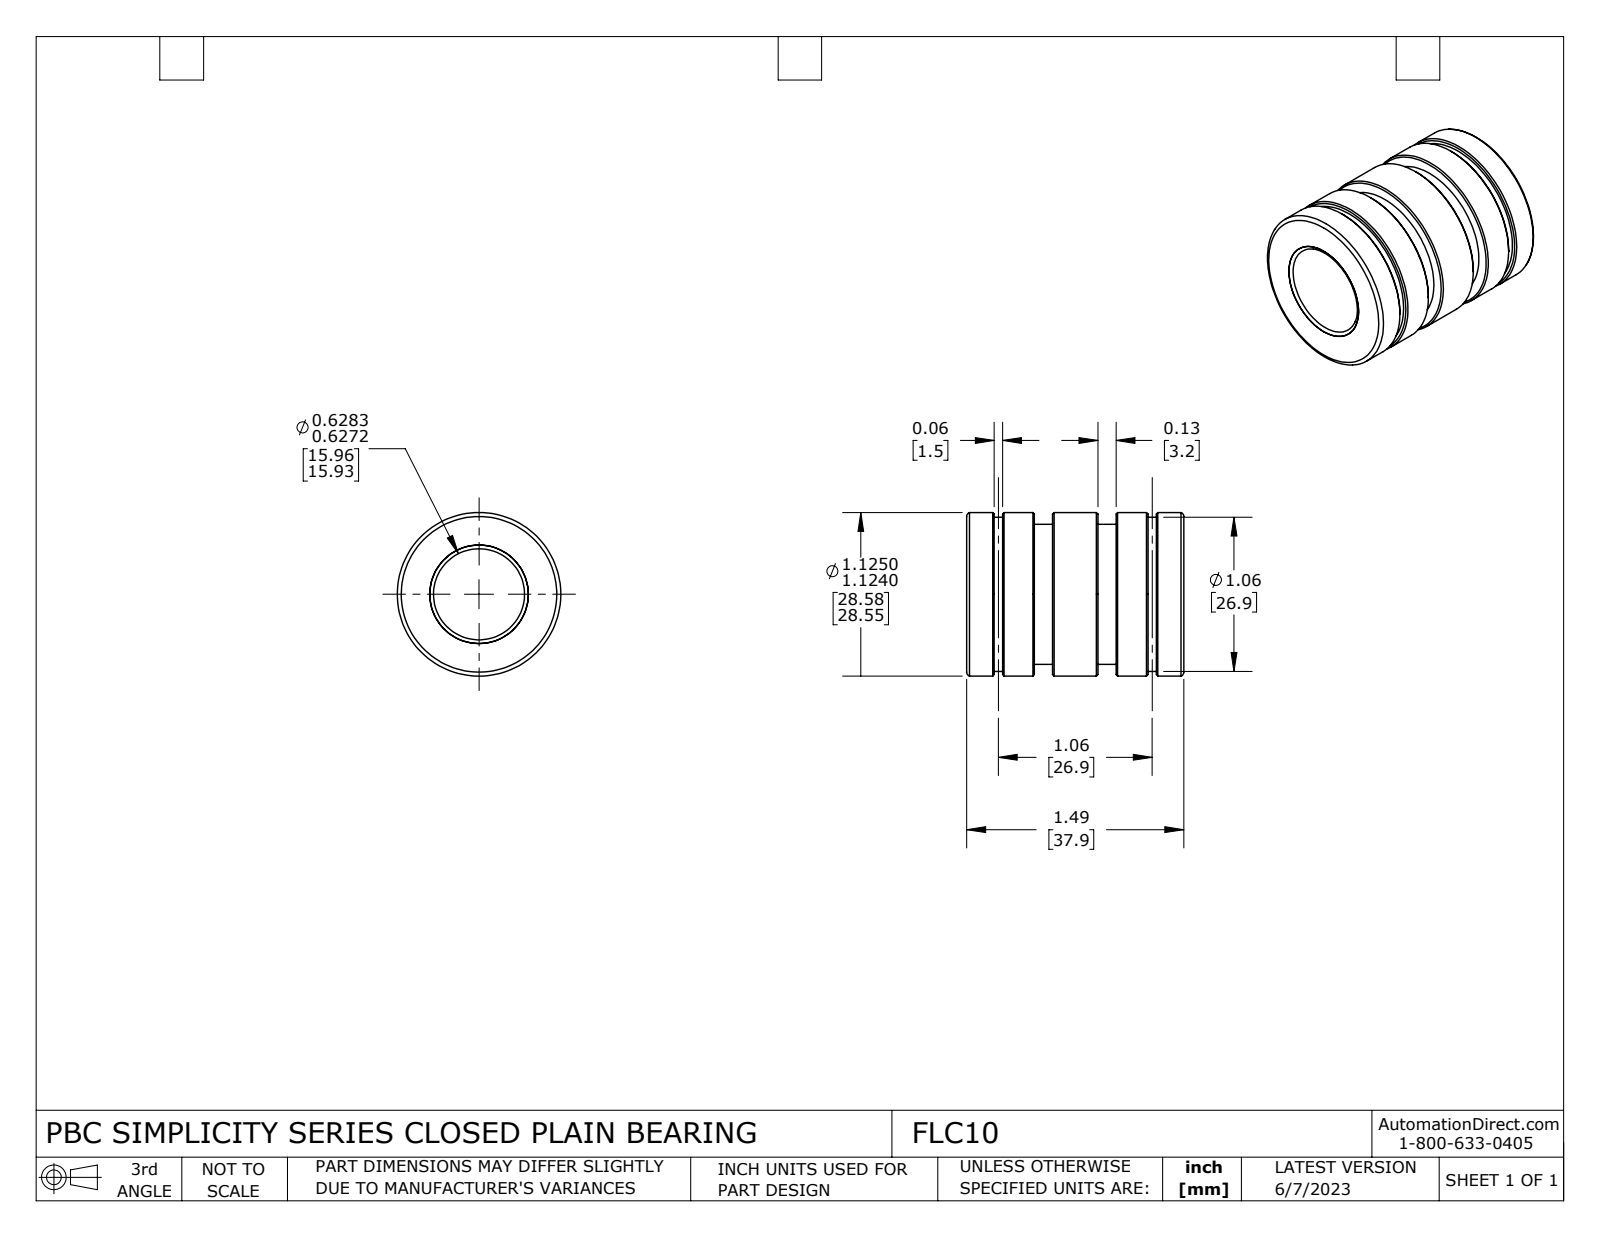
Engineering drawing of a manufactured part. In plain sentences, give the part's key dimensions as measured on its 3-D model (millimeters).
The part is named "FLC10". Its 3-D file was written by "SolidWorks 2021 (CONFIG_CONTROL_DESIGN)". It is 2 solids with 58 faces: 10 planar, 24 cylindrical and 24 other. Overall it measures 37.9 by 28.5 by 28.5 millimeters. Its volume is 15 400 cubic millimeters and its surface area 10 960 square millimeters. Round holes: 1 of diameter 15.9, 1 of diameter 17.2. Round bosses or shafts: 1 of diameter 28.5, 1 of diameter 26.9, 1 of diameter 24.4. The main face-to-face distances are 37.9, 15, 22.9, 11.8, 26.1, 3.2, 11.1, 7.9, 14.3, 6.2.
